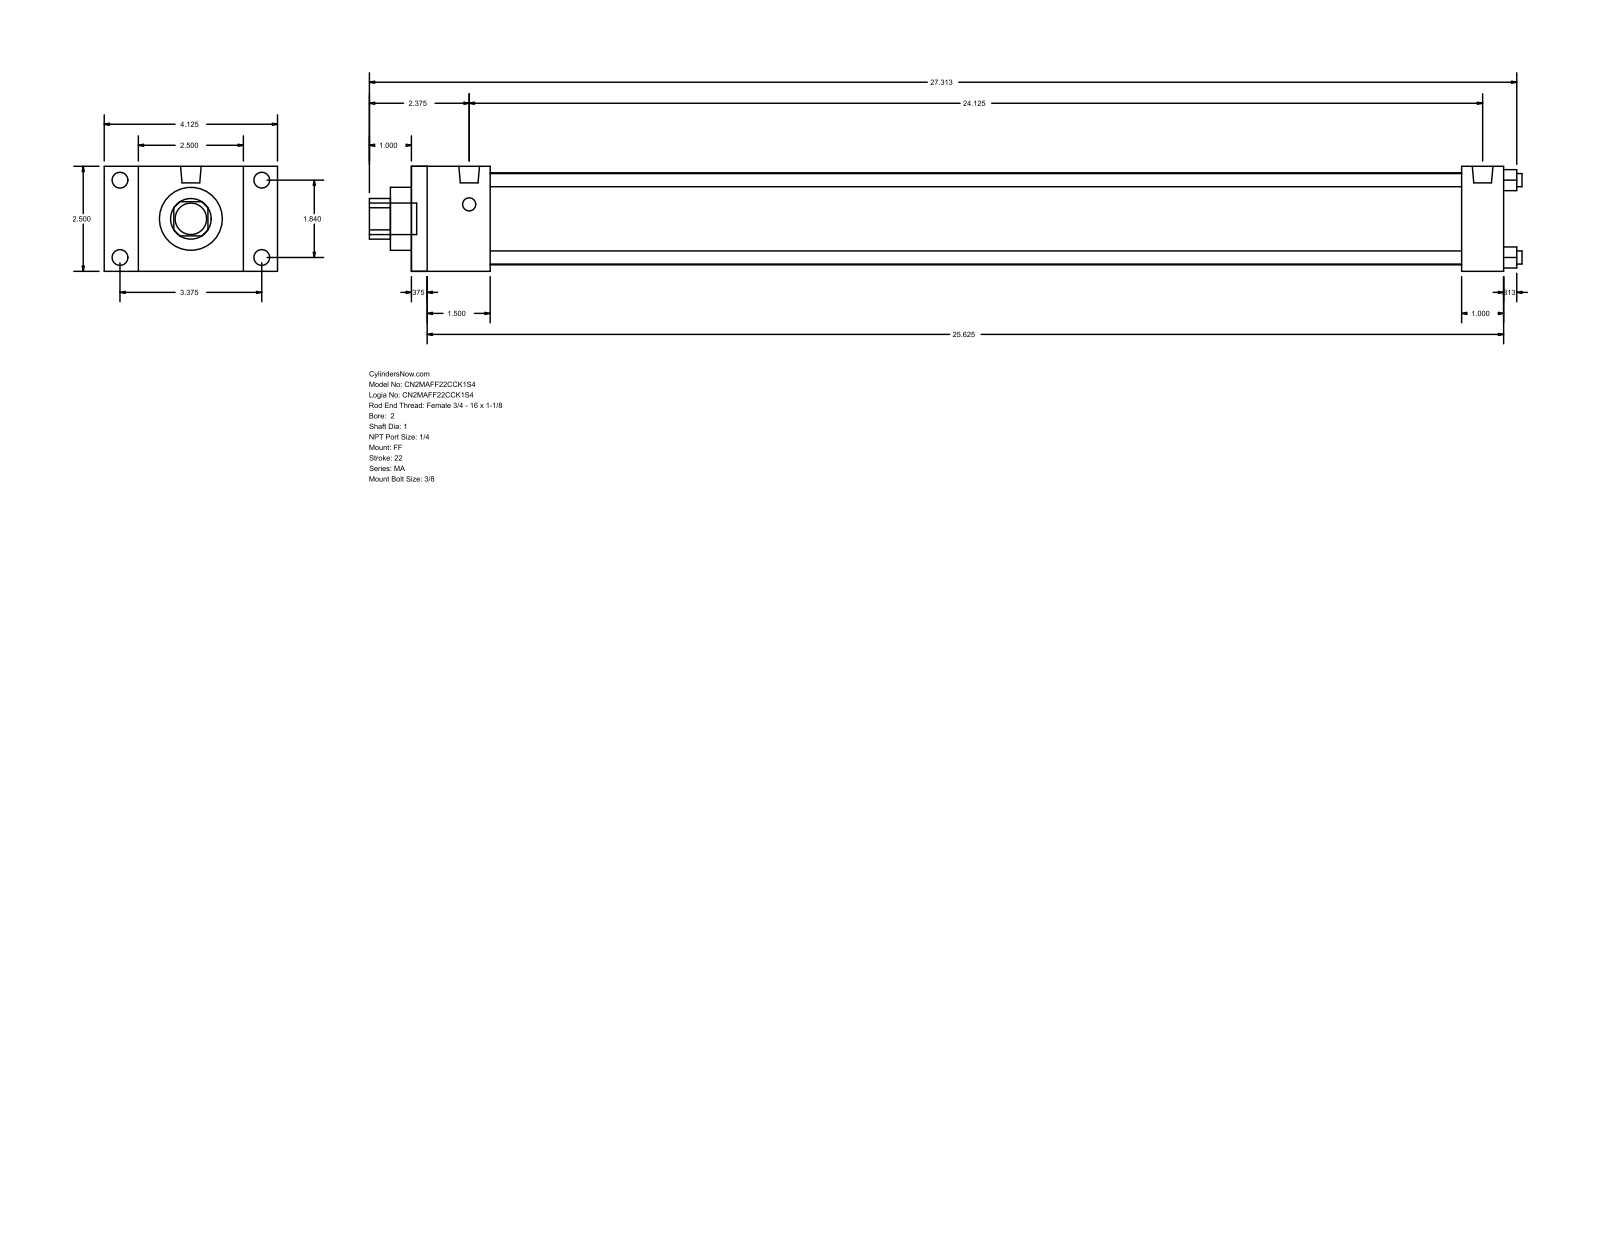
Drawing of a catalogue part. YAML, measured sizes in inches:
part_name: "MA_FF__0200_1"
step_written_by: "GSSL Pune (CONFIG_CONTROL_DESIGN)"
units: inches
bodies: {solids: 0, faces: 92, planar: 64, cylindrical: 28, other: 0}
overall_size: [27.437, 4.125, 2.5]
round_holes:
  - {diameter: 0.313, count: 4}
  - {diameter: 1, count: 1}
  - {diameter: 1.5, count: 1}
  - {diameter: 2.19, count: 1}
round_bosses_or_shafts:
  - {diameter: 0.375, count: 4}
  - {diameter: 0.313, count: 4}
  - {diameter: 0.492, count: 2}
  - {diameter: 0.75, count: 1}
partial_cylinders:
  - {radius: 0.484, count: 1}
face_to_face_distances: [2.5, 26, 0.375, 25.625, 1, 0.813, 0.5, 1.875, 25, 1.5]
hole_center_spacings: [1.301, 1.84, 2.602]
